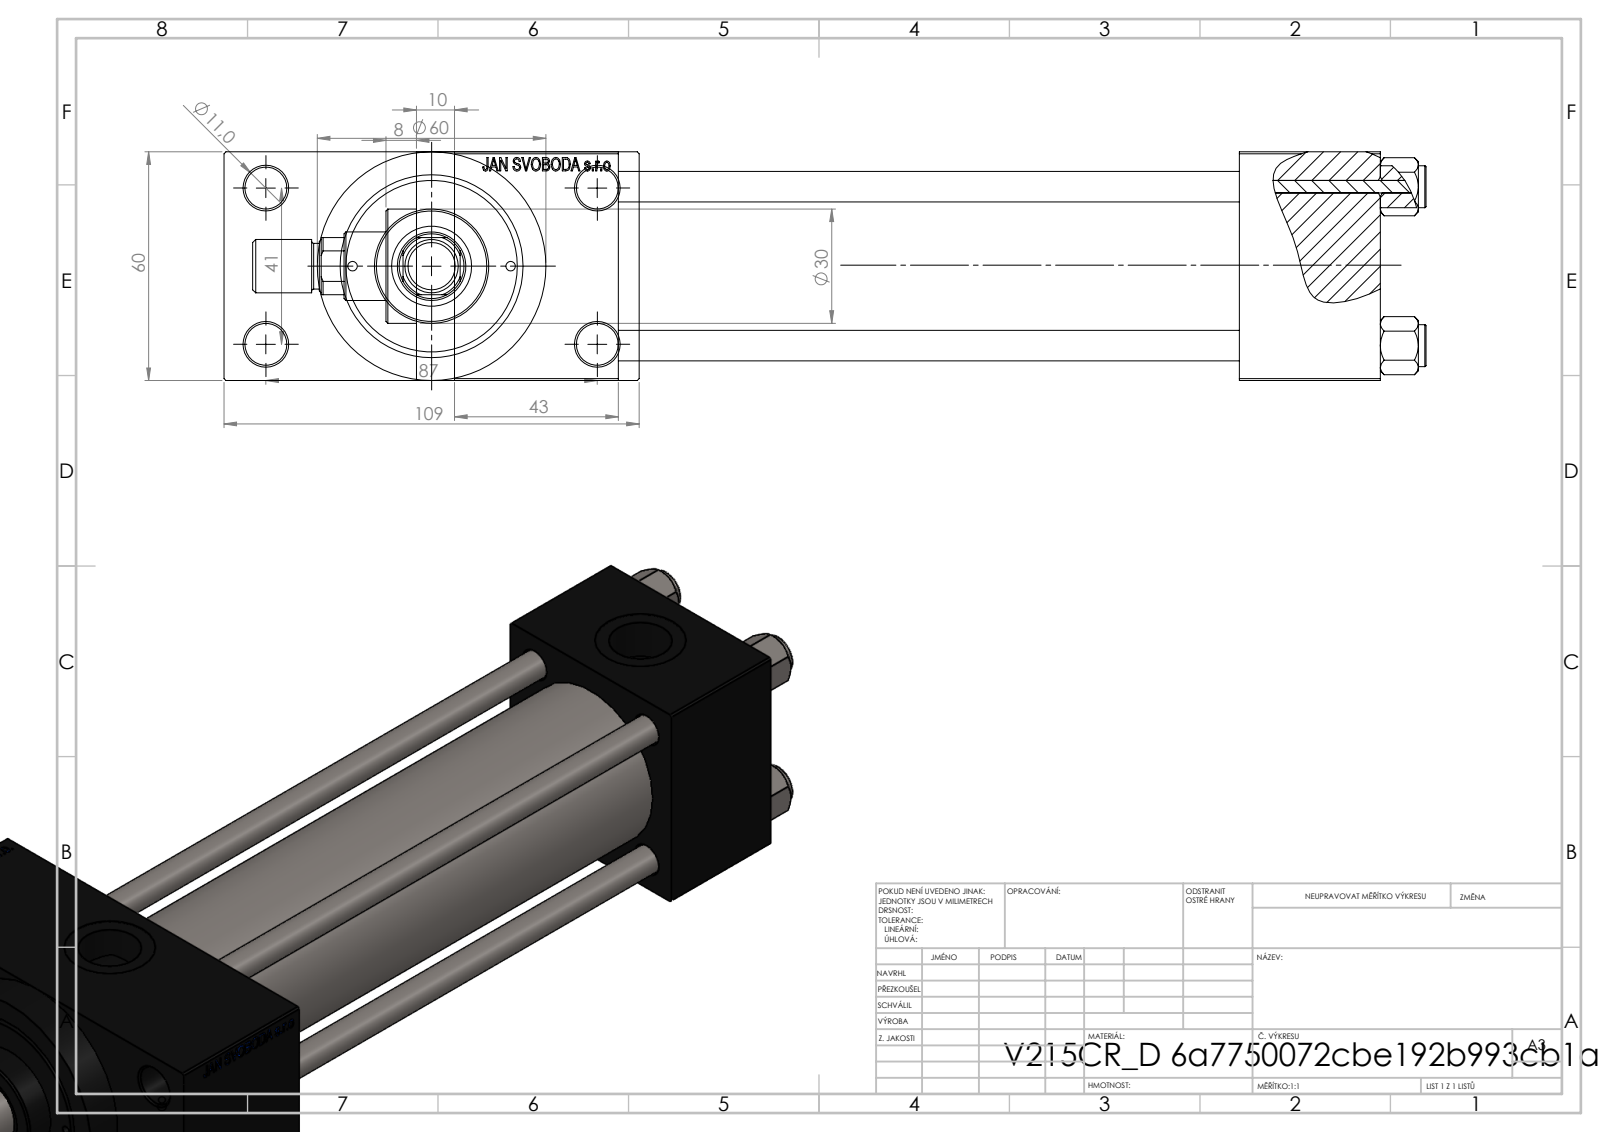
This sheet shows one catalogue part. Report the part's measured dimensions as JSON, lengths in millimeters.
{"part_name": "V215_VC_A; V215CR_VCP_D; ROD_END_AH; NUT_M5_D (+2 more)", "step_written_by": "SolidWorks 2019 (CONFIG_CONTROL_DESIGN)", "units": "millimeters", "bodies": {"solids": 12, "faces": 1127, "planar": 504, "cylindrical": 97, "other": 526}, "overall_size": [308, 109, 60], "volume_mm3": 610610, "surface_area_mm2": 167212, "round_holes": [[8, 4], [11, 4], [2.5, 2], [7, 2], [16.66, 2], [24, 2], [8.5, 1], [18, 1], [21, 1], [31, 1], [40, 1], [45, 1]], "round_bosses_or_shafts": [[11, 4], [60, 1], [46, 1], [30, 1], [14, 1], [12, 1]], "partial_cylinders_radius": [[8.5, 1]], "face_to_face_distances": [60, 24.5, 84.5, 163, 37, 200, 43, 243, 206, 109], "hole_center_spacings": [20.85, 22.65, 29.49, 30.62, 41.7, 46.53, 47.15, 48.09]}
